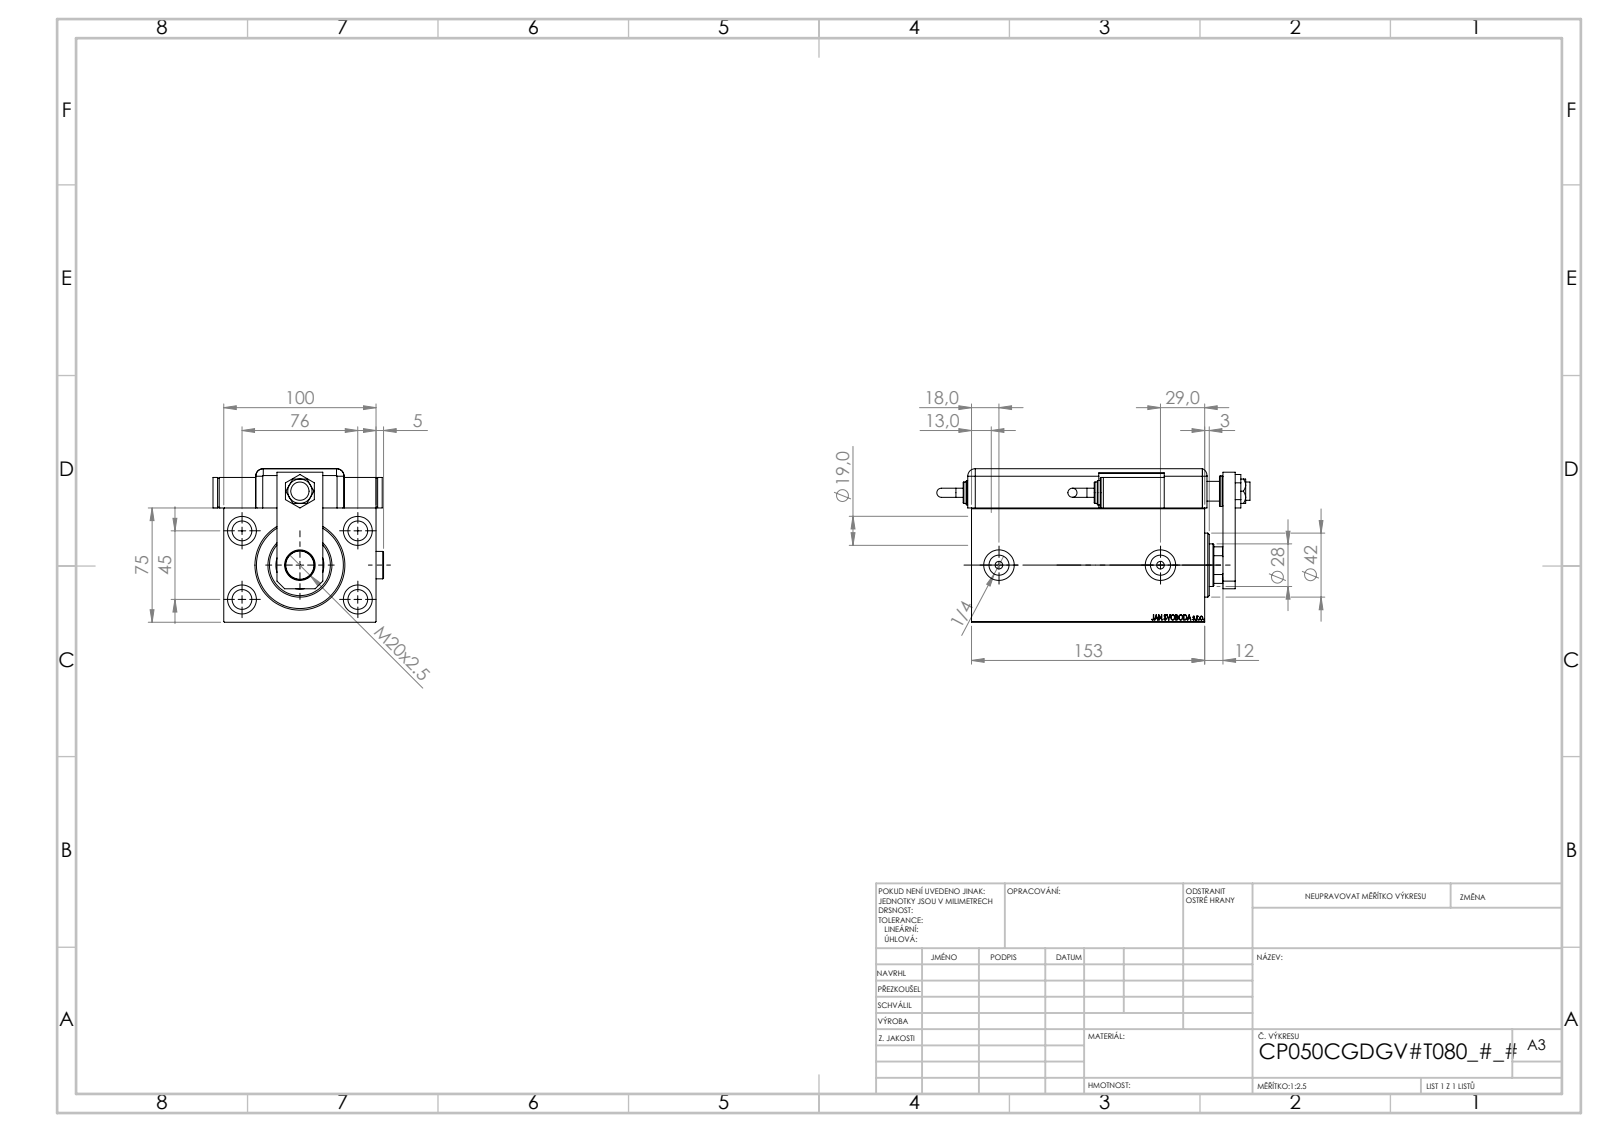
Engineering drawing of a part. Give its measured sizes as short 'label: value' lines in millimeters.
name: NUT_D19; KRYT; V450CM_C_VCP; ZARAZKA_Q (+7 more)
written by: SolidWorks 2019 (CONFIG_CONTROL_DESIGN)
unit: mm
bodies: 15 solids, 1303 faces (649 planar, 133 cylindrical, 521 other)
size: 205.46 × 111.9 × 100.8
volume: 1 106 000 mm³; area: 218 099 mm²
holes: 5× ⌀13, 4× ⌀19, 3× ⌀20, 2× ⌀4, 2× ⌀5, 2× ⌀8, 2× ⌀13.16, 1× ⌀12, 1× ⌀14, 1× ⌀18.5, 1× ⌀28, 1× ⌀31.5
bosses: 3× ⌀20, 2× ⌀18, 2× ⌀16, 2× ⌀14, 2× ⌀6, 1× ⌀42
rounds: 9× R5, 1× R10, 1× R13.5
face distances: 75, 3, 100, 25.8, 100.8, 24, 97.8, 22.8, 14, 79
hole spacings: 44.16, 45, 46.04, 76, 80.53, 88.32, 20, 48.5
